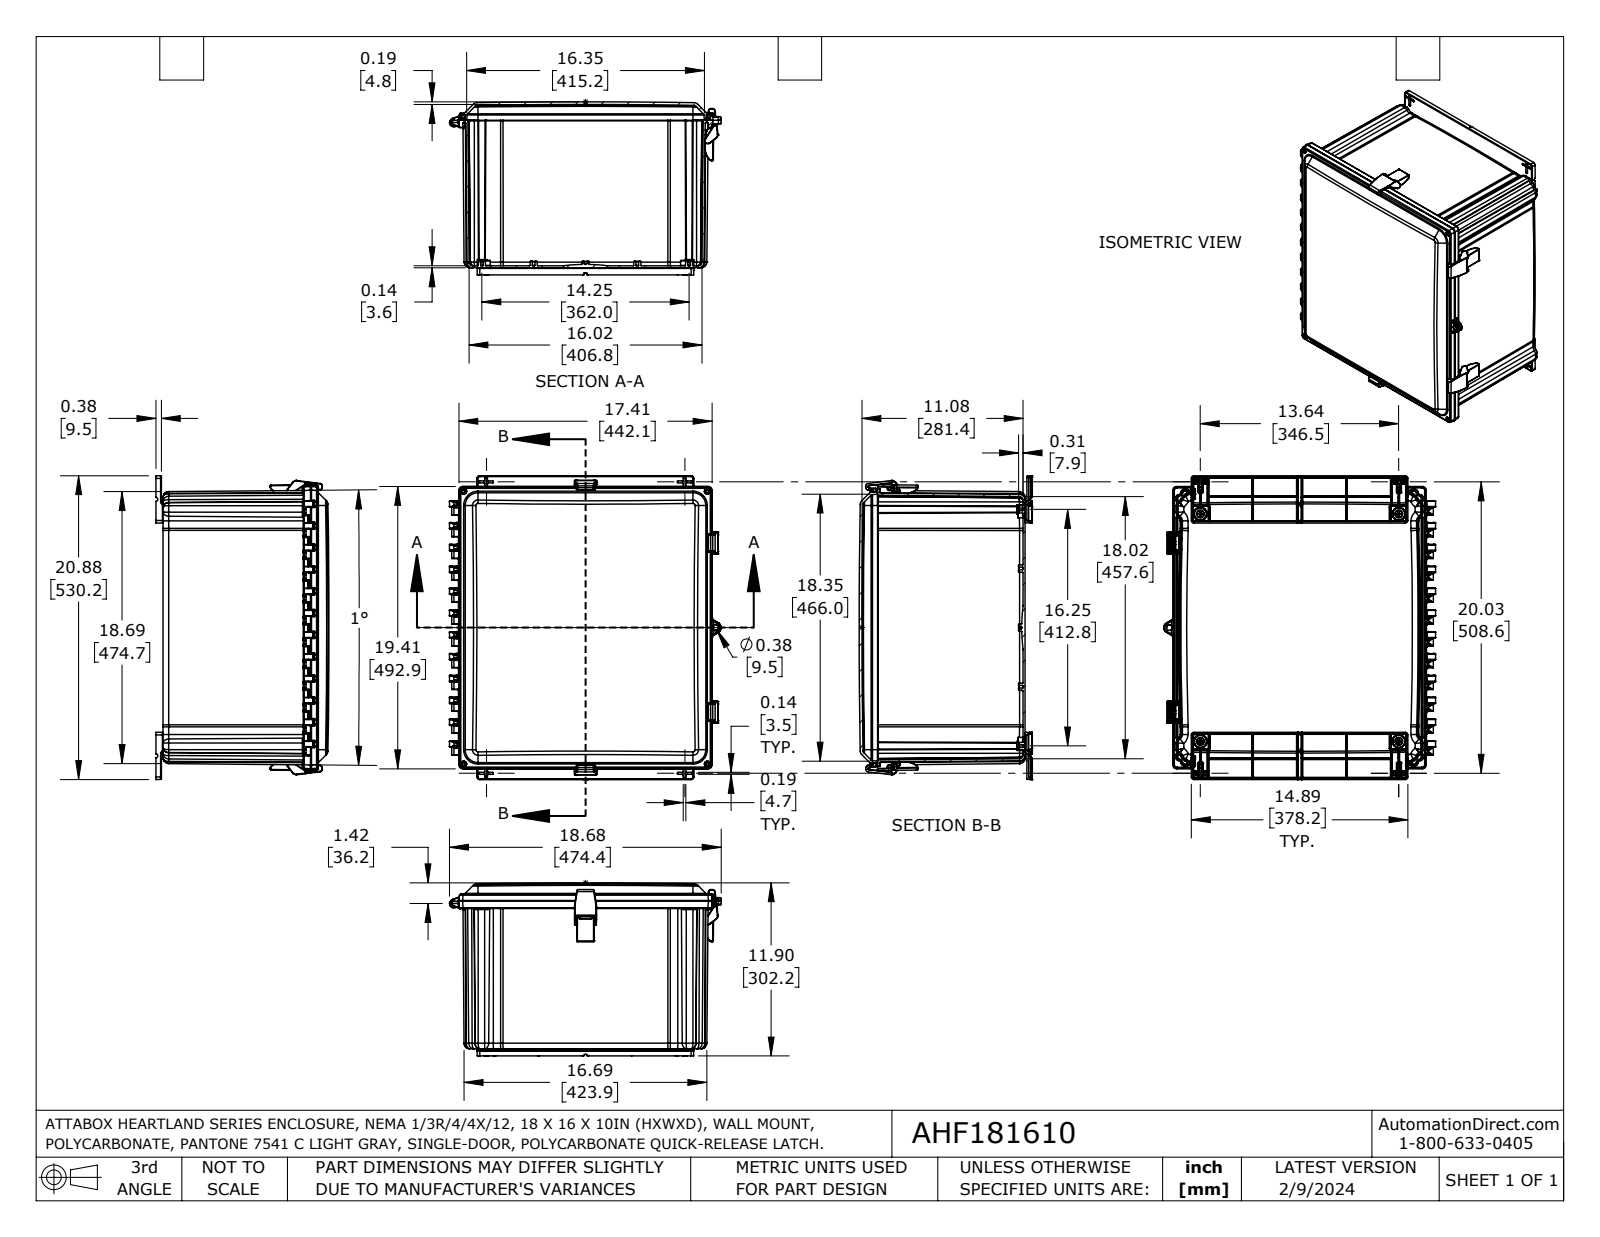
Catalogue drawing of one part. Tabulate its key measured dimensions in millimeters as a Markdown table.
| quantity | value |
| --- | --- |
| part name | AHF181610C |
| STEP written by | SolidWorks 2023 (AUTOMOTIVE_DESIGN) |
| units | millimeters |
| bodies | 10 solids, 2440 faces (778 planar, 796 cylindrical, 866 other) |
| overall size | 529.8 × 474.4 × 302.5 |
| volume | 4 420 000 mm³ |
| surface area | 2 079 000 mm² |
| round holes (diameter × count) | 4.7 × 21, 5 × 4, 6.4 × 4, 7.1 × 4, 9.9 × 4, 9.5 × 2, 6.9 × 1, 8.3 × 1, 11.4 × 1 |
| round bosses / shafts (diameter × count) | 12.4 × 21, 5.1 × 6, 15.9 × 4, 8 × 1, 6.4 × 1 |
| partial cylindrical surfaces (radius × count) | 0.9 × 338, 1.7 × 49, 0.3 × 46, 0.5 × 21, 0.6 × 9, 1.3 × 8, 8.8 × 8, 2.4 × 6 |
| main face-to-face distances | 2.7, 409.1, 3.6, 459.9, 406.4, 12.7, 457.2, 411.8, 257.6, 462.6 |
| hole center spacings | 103.2, 137.3, 274.5, 322.5, 206.4, 225.3, 137.2, 208.3 |
